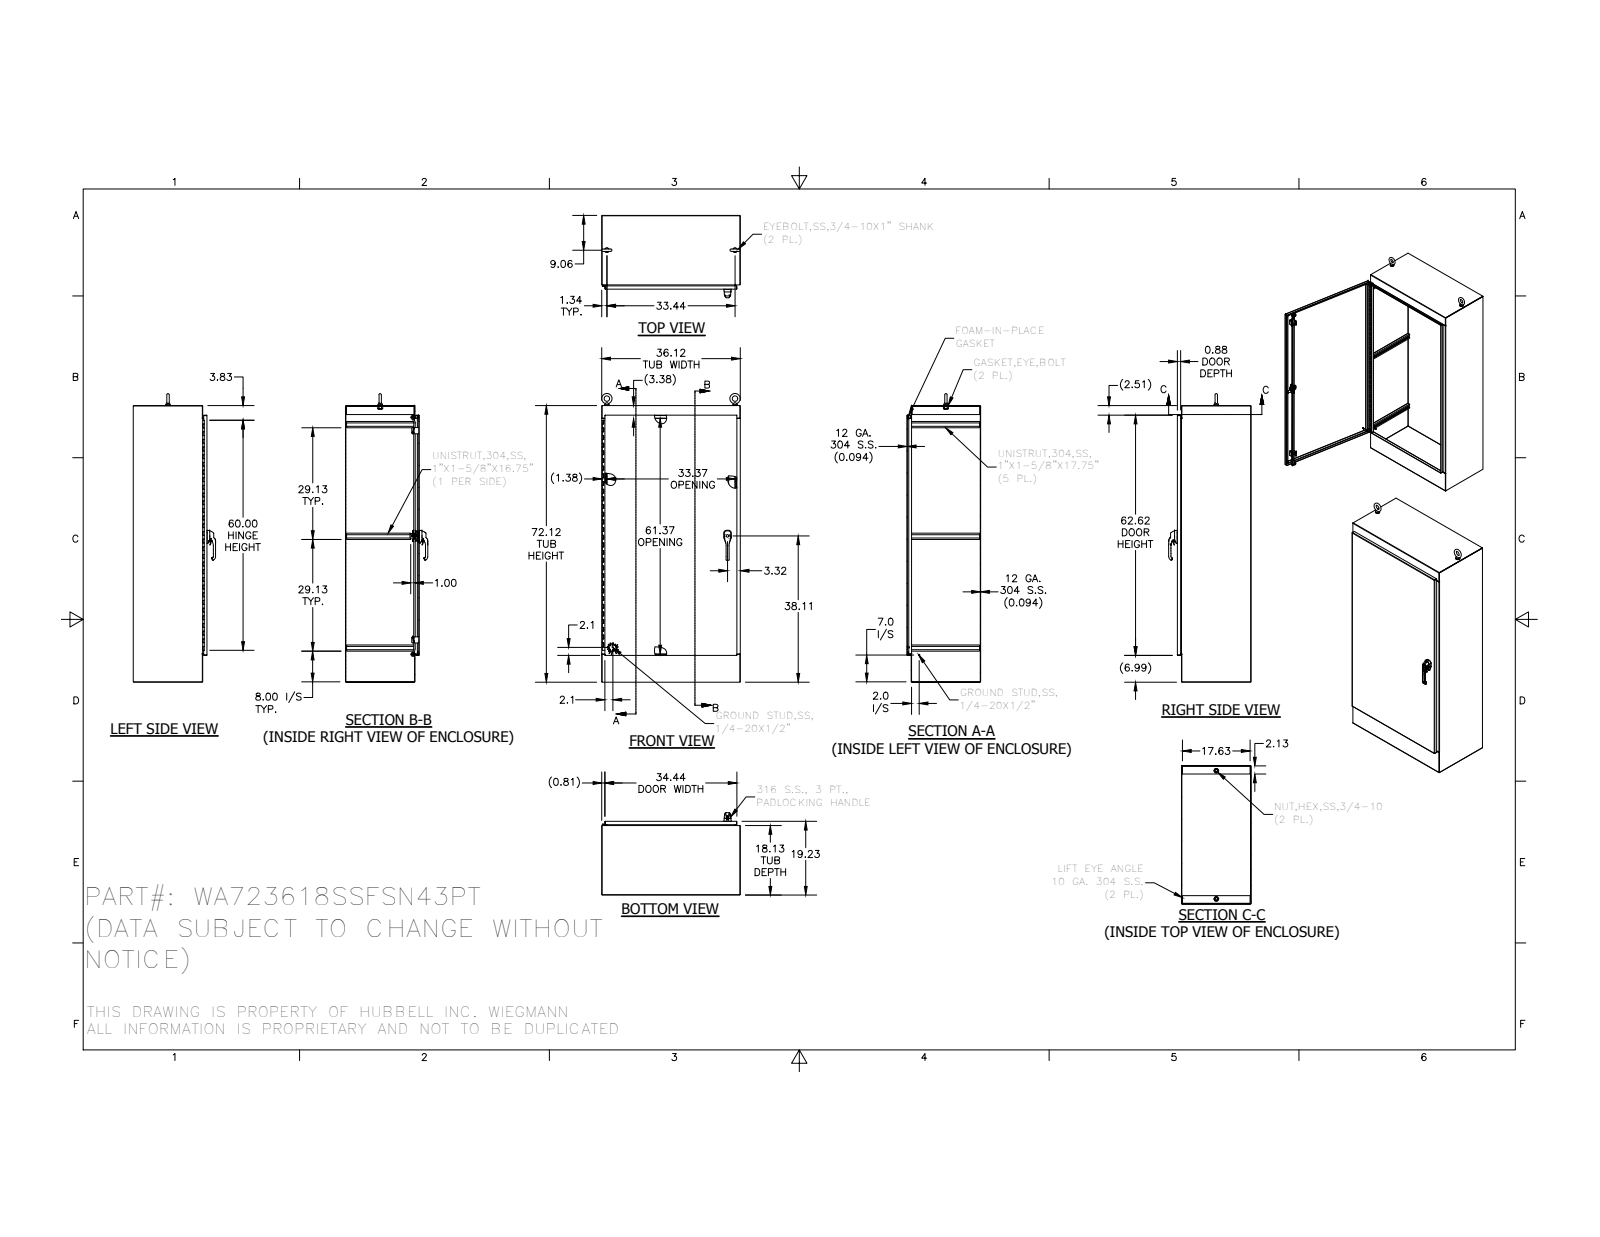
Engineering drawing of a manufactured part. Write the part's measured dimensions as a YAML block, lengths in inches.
part_name: "PLASTIC-ROLLER-CAM_AF1; 328131-60; SPACER; 1091-903_AF0_1 (+8 more)"
step_written_by: "SolidWorks 2014 (AUTOMOTIVE_DESIGN)"
units: inches
bodies: {solids: 65, faces: 3473, planar: 1224, cylindrical: 1309, other: 940}
overall_size: [75.248, 36.125, 21.476]
volume: 1036
surface_area: 21432
round_holes:
  - {diameter: 0.262, count: 8}
  - {diameter: 0.375, count: 8}
  - {diameter: 0.187, count: 4}
  - {diameter: 0.213, count: 3}
  - {diameter: 0.25, count: 3}
  - {diameter: 0.28, count: 3}
  - {diameter: 0.241, count: 2}
  - {diameter: 0.252, count: 2}
  - {diameter: 0.315, count: 2}
  - {diameter: 0.4, count: 2}
  - {diameter: 0.402, count: 2}
  - {diameter: 0.413, count: 2}
round_bosses_or_shafts:
  - {diameter: 1, count: 3}
  - {diameter: 0.236, count: 3}
  - {diameter: 1.25, count: 2}
  - {diameter: 1.12, count: 2}
  - {diameter: 0.75, count: 2}
  - {diameter: 0.563, count: 2}
  - {diameter: 0.533, count: 2}
  - {diameter: 0.531, count: 2}
partial_cylinders:
  - {radius: 0.02, count: 172}
  - {radius: 0.012, count: 106}
  - {radius: 0.125, count: 26}
  - {radius: 0.019, count: 21}
  - {radius: 0.05, count: 19}
  - {radius: 0.031, count: 18}
  - {radius: 0.079, count: 14}
  - {radius: 0.125, count: 14}
face_to_face_distances: [0.094, 19.133, 36.031, 19.039, 19.227, 35.937, 72.031, 36.125, 18.031, 1.102]
hole_center_spacings: [20, 0.76, 6.667, 13.333, 0.38, 0.38, 6.667, 54.178]
